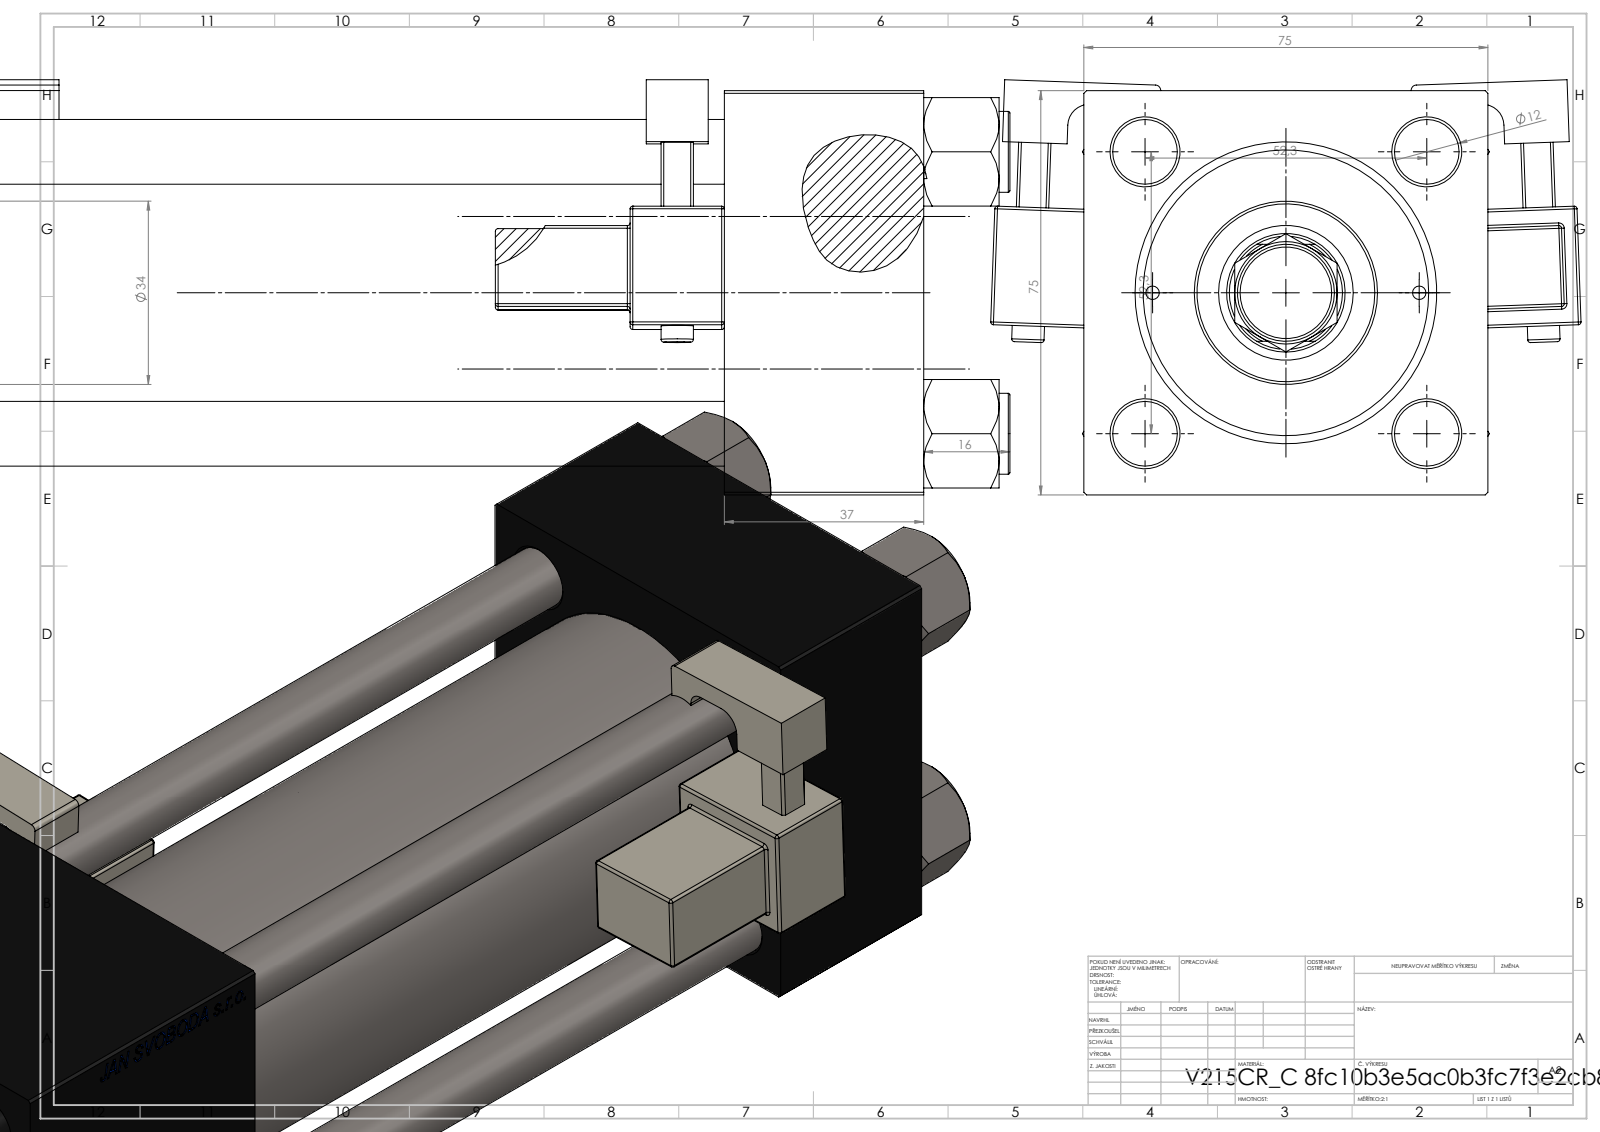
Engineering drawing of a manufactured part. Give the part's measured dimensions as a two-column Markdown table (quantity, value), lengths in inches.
| quantity | value |
| --- | --- |
| part name | V215CR_C_Body; V215_VC_A; V215CR_C_TYCINKA; V215CR_MSU (+3 more) |
| STEP written by | SolidWorks 2019 (CONFIG_CONTROL_DESIGN) |
| units | inches |
| bodies | 14 solids, 1360 faces (602 planar, 154 cylindrical, 604 other) |
| overall size | 12.126 × 4.314 × 3.033 |
| volume | 49.59 in³ |
| surface area | 320.2 in² |
| round holes (diameter × count) | 0.472 × 4, 0.098 × 2, 0.276 × 2, 0.825 × 2, 1.181 × 2, 0.413 × 1, 0.866 × 1, 0.984 × 1, 1.614 × 1, 1.969 × 1, 2.087 × 1 |
| round bosses / shafts (diameter × count) | 0.591 × 4, 0.236 × 2, 2.205 × 1, 1.339 × 1, 0.709 × 1, 0.433 × 1 |
| partial cylindrical surfaces (radius × count) | 0.02 × 48, 0.039 × 2, 0.098 × 2, 0.157 × 2, 0.413 × 1 |
| main face-to-face distances | 2.953, 1.457, 9.213, 7.756, 6.89, 5.433, 2.323, 8.083, 6.626, 1.193 |
| hole center spacings | 1.031, 1.456, 2.059, 2.253, 0.974, 2.912, 1.949, 6.831 |
